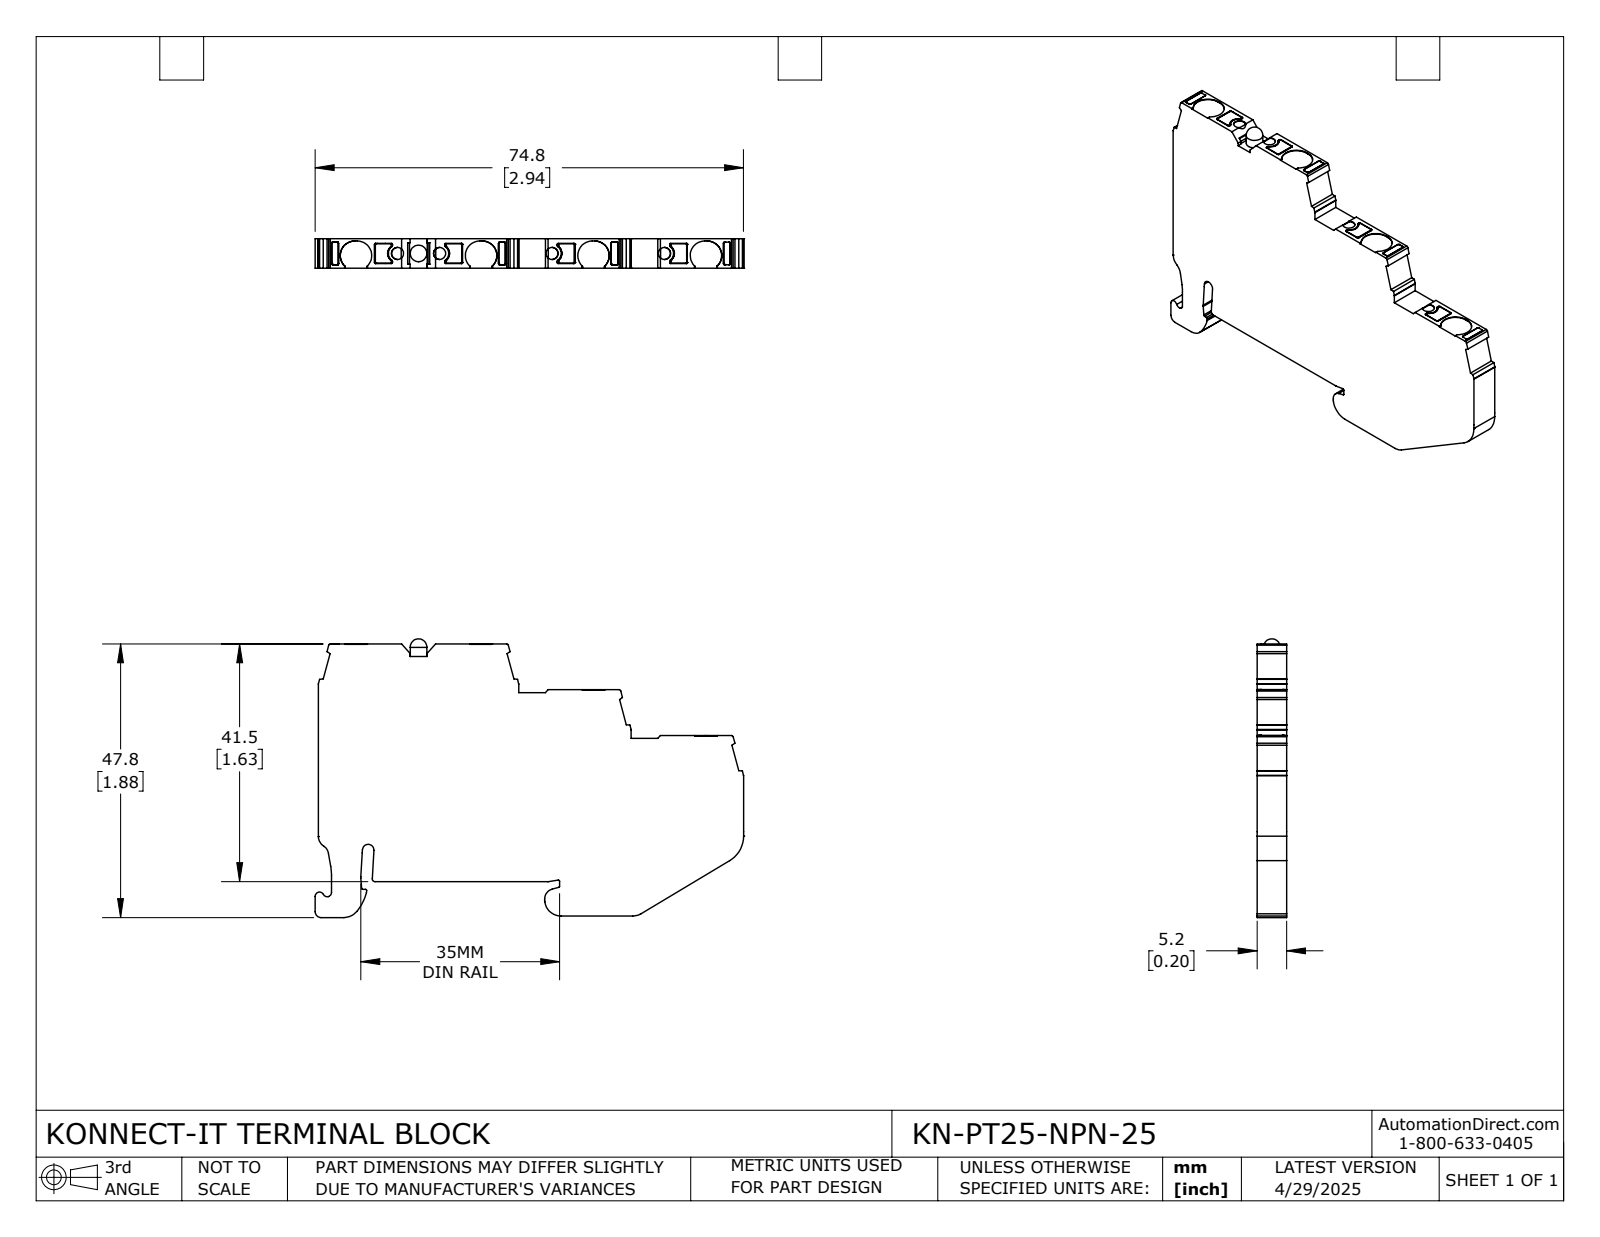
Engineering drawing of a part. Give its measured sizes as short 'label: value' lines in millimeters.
name: KN-PT25-NPN-25
written by: SolidWorks 2024 (CONFIG_CONTROL_DESIGN)
unit: mm
bodies: 1 solid, 358 faces (201 planar, 146 cylindrical, 11 other)
size: 74.8 × 48.65 × 5.15
volume: 13 781 mm³; area: 6 772 mm²
holes: 4× ⌀2.1
bosses: 1× ⌀2.9
rounds: 68× R0.2, 16× R0.15, 8× R0.3, 8× R2.55, 4× R1.5, 4× R1.55, 3× R1, 3× R2
face distances: 5.15, 8, 6, 16, 7.99, 15.99, 74.25, 7.9, 8.1, 0.4
hole spacings: 7.34, 19.63, 19.64, 26.98, 39.27, 46.61
